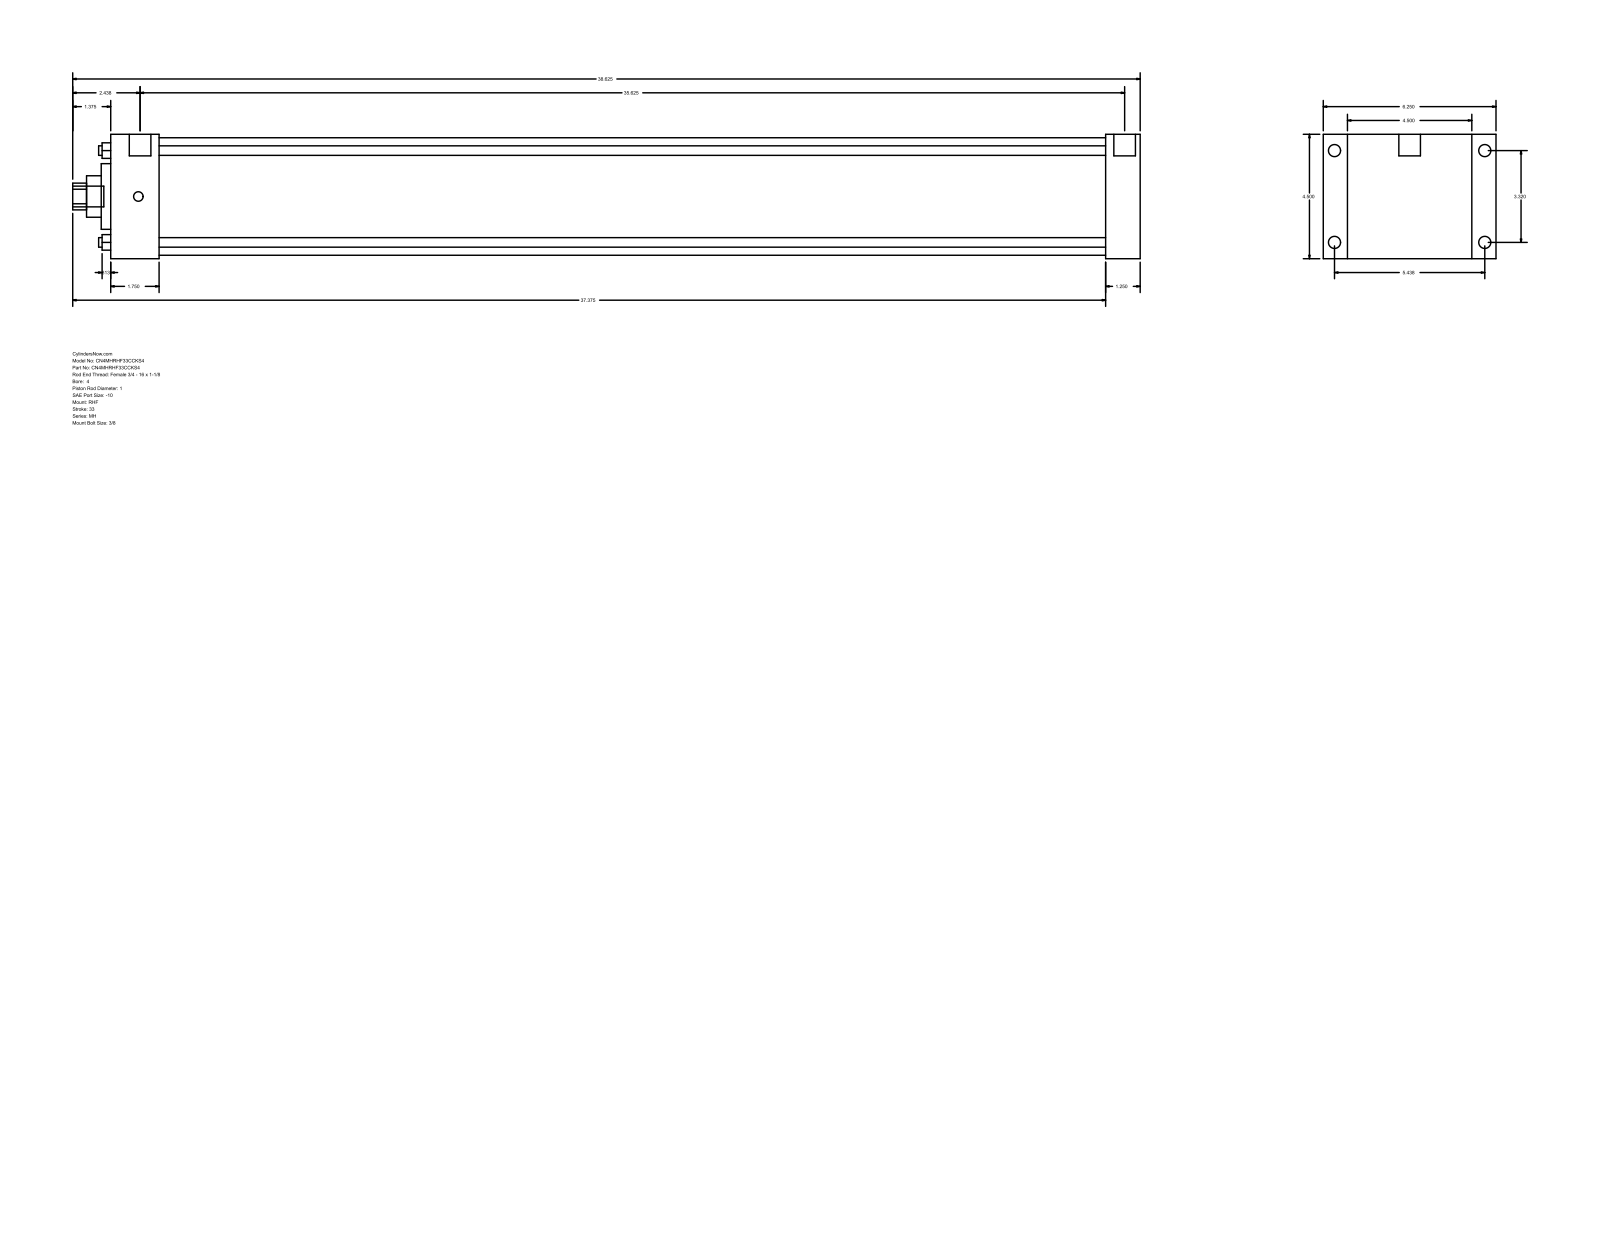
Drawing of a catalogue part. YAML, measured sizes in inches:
part_name: "MH_RHF__0400_1"
step_written_by: "GSSL Pune (CONFIG_CONTROL_DESIGN)"
units: inches
bodies: {solids: 0, faces: 90, planar: 61, cylindrical: 29, other: 0}
overall_size: [38.625, 6.25, 4.5]
round_holes:
  - {diameter: 0.345, count: 4}
  - {diameter: 1, count: 1}
  - {diameter: 1.5, count: 1}
  - {diameter: 2.375, count: 1}
  - {diameter: 4.25, count: 1}
round_bosses_or_shafts:
  - {diameter: 0.438, count: 4}
  - {diameter: 0.344, count: 4}
  - {diameter: 0.781, count: 2}
  - {diameter: 0.75, count: 1}
partial_cylinders:
  - {radius: 0.484, count: 1}
face_to_face_distances: [4.5, 37.25, 36, 1.25, 0.875, 5.375, 1.75, 34.25, 35.5, 6.25]
hole_center_spacings: [2.347, 3.32, 4.695]
